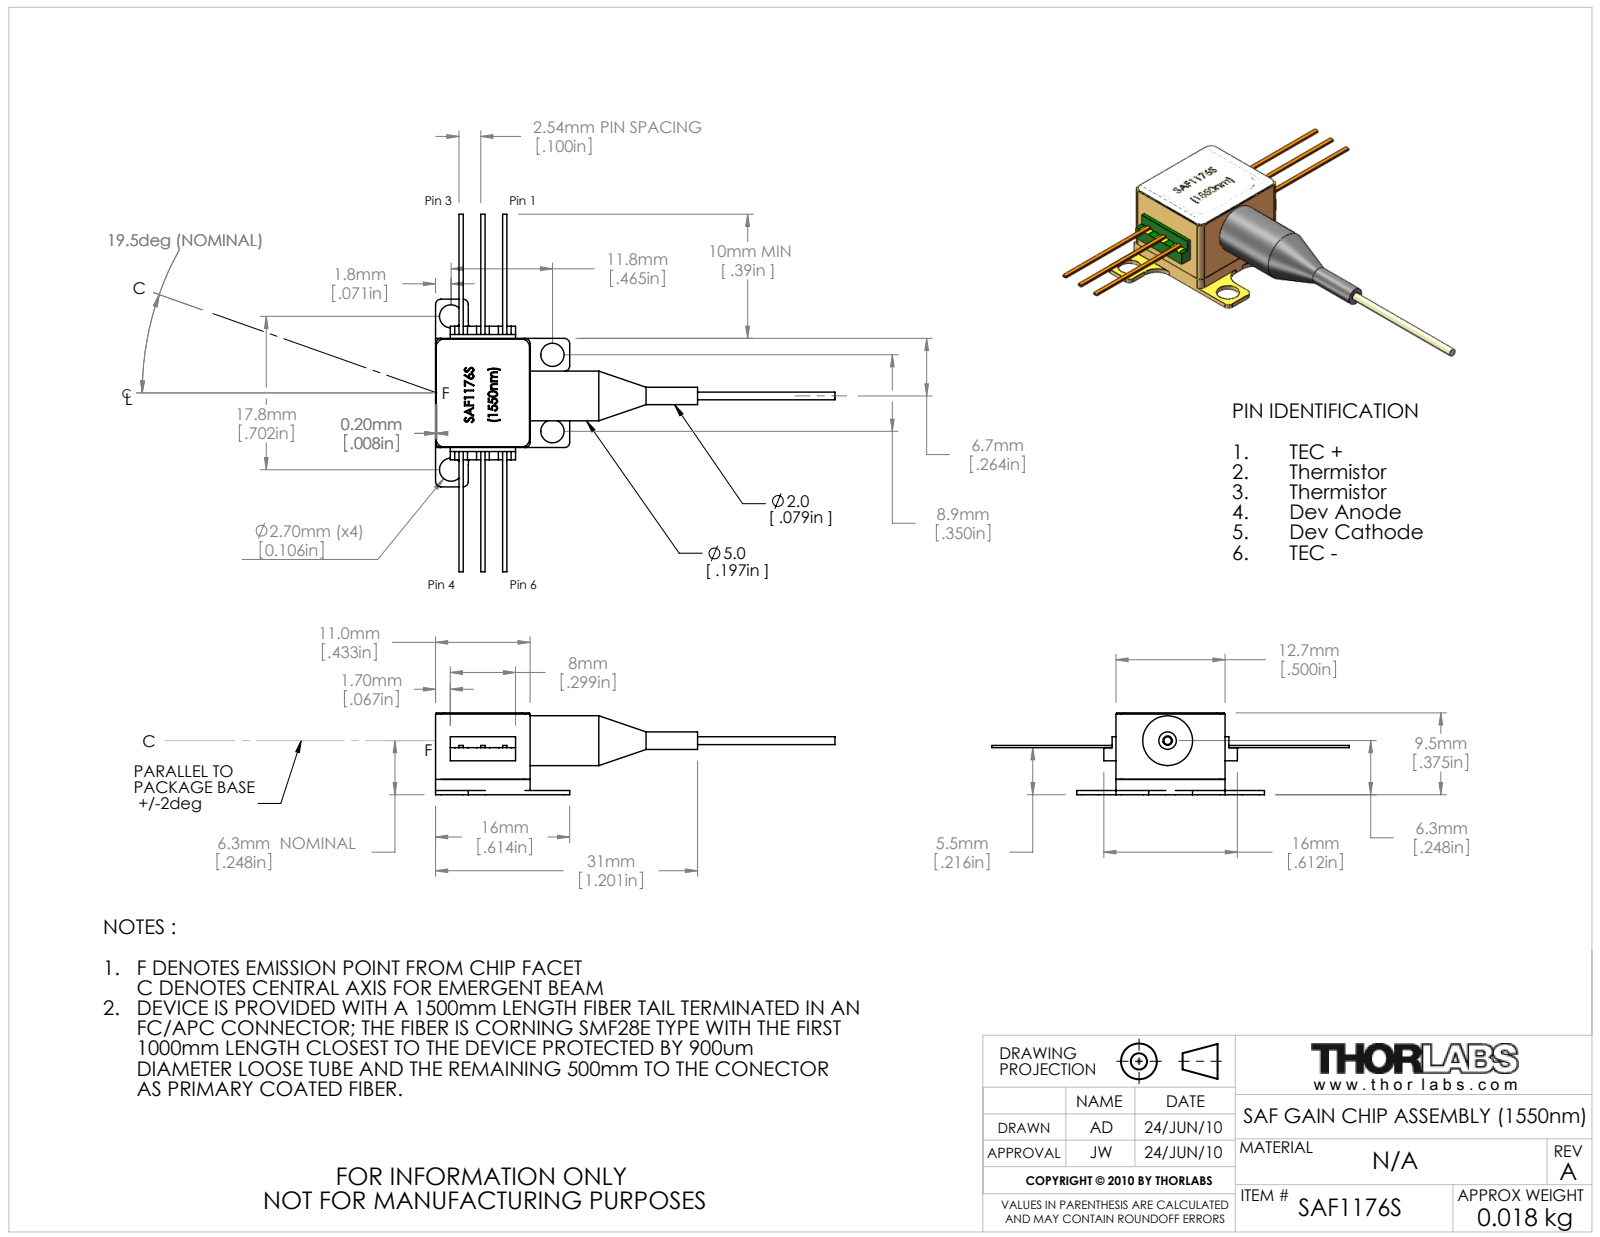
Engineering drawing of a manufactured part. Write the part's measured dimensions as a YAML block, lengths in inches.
part_name: "20746-E0W"
step_written_by: "SolidWorks 2009 (AUTOMOTIVE_DESIGN)"
units: inches
bodies: {solids: 15, faces: 465, planar: 302, cylindrical: 70, other: 93}
overall_size: [1.831, 1.638, 0.375]
volume: 0.057
surface_area: 3.757
round_holes:
  - {diameter: 0.106, count: 4}
  - {diameter: 0.043, count: 1}
  - {diameter: 0.082, count: 1}
  - {diameter: 0.125, count: 1}
  - {diameter: 0.161, count: 1}
round_bosses_or_shafts:
  - {diameter: 0.228, count: 1}
  - {diameter: 0.136, count: 1}
  - {diameter: 0.08, count: 1}
  - {diameter: 0.035, count: 1}
partial_cylinders:
  - {radius: 0.024, count: 12}
  - {radius: 0.039, count: 10}
  - {radius: 0.005, count: 4}
  - {radius: 0.012, count: 4}
  - {radius: 0.035, count: 4}
  - {radius: 0.073, count: 4}
  - {radius: 0.079, count: 4}
face_to_face_distances: [0.039, 0.063, 0.375, 0.312, 0.299, 0.37, 0.307, 0.071, 0.057, 0.461]
hole_center_spacings: [0.497, 0.702, 0.35, 0.702]
